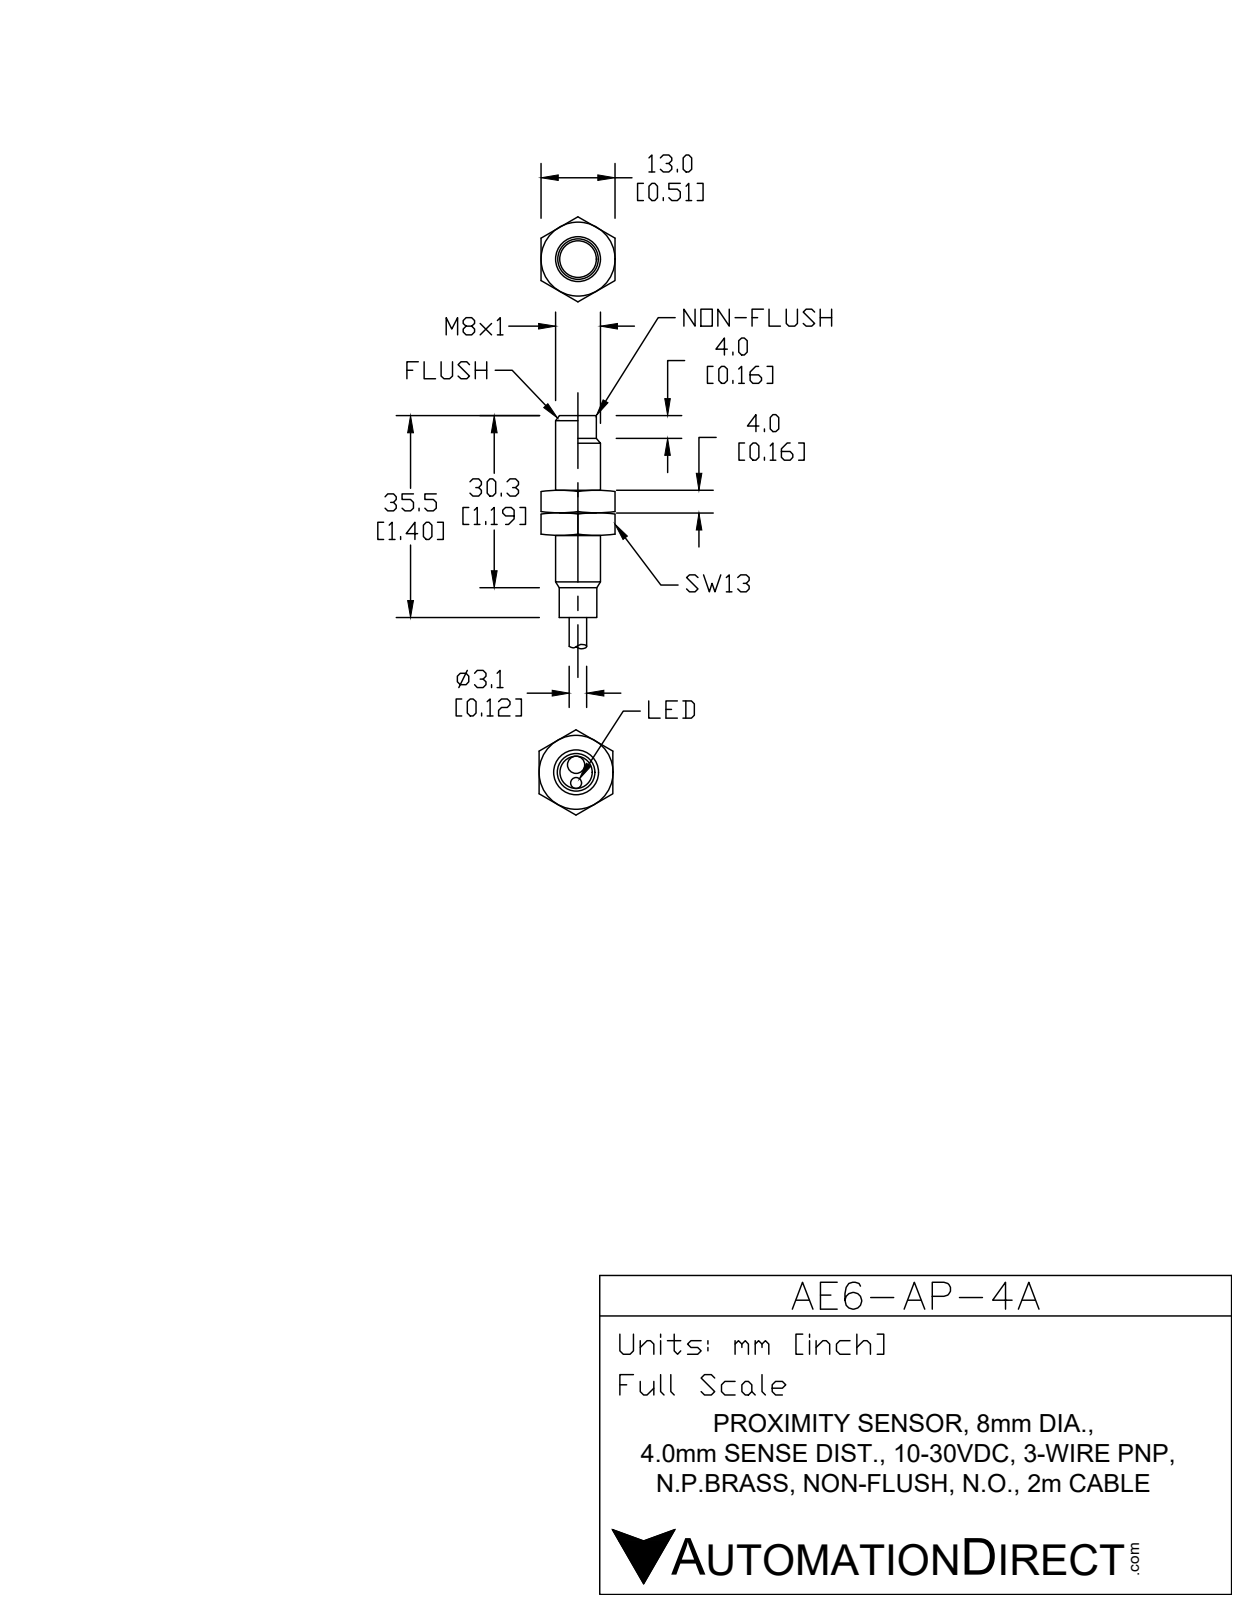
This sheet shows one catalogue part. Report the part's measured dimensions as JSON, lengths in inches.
{"part_name": "AE6-AP-4A", "step_written_by": "SolidWorks 2017 (AUTOMOTIVE_DESIGN)", "units": "inches", "bodies": {"solids": 4, "faces": 30, "planar": 10, "cylindrical": 12, "other": 8}, "overall_size": [2.933, 0.315, 0.315], "volume_in3": 0.116, "surface_area_in2": 2.281, "round_holes": [[0.122, 1], [0.228, 1]], "round_bosses_or_shafts": [[0.315, 1], [0.256, 1], [0.254, 1]], "face_to_face_distances": [1.031, 0.157, 1.189, 1.378, 1.22, 0.189, 0.02, 1.358, 1.201, 0.169], "hole_center_spacings": [0.045]}
